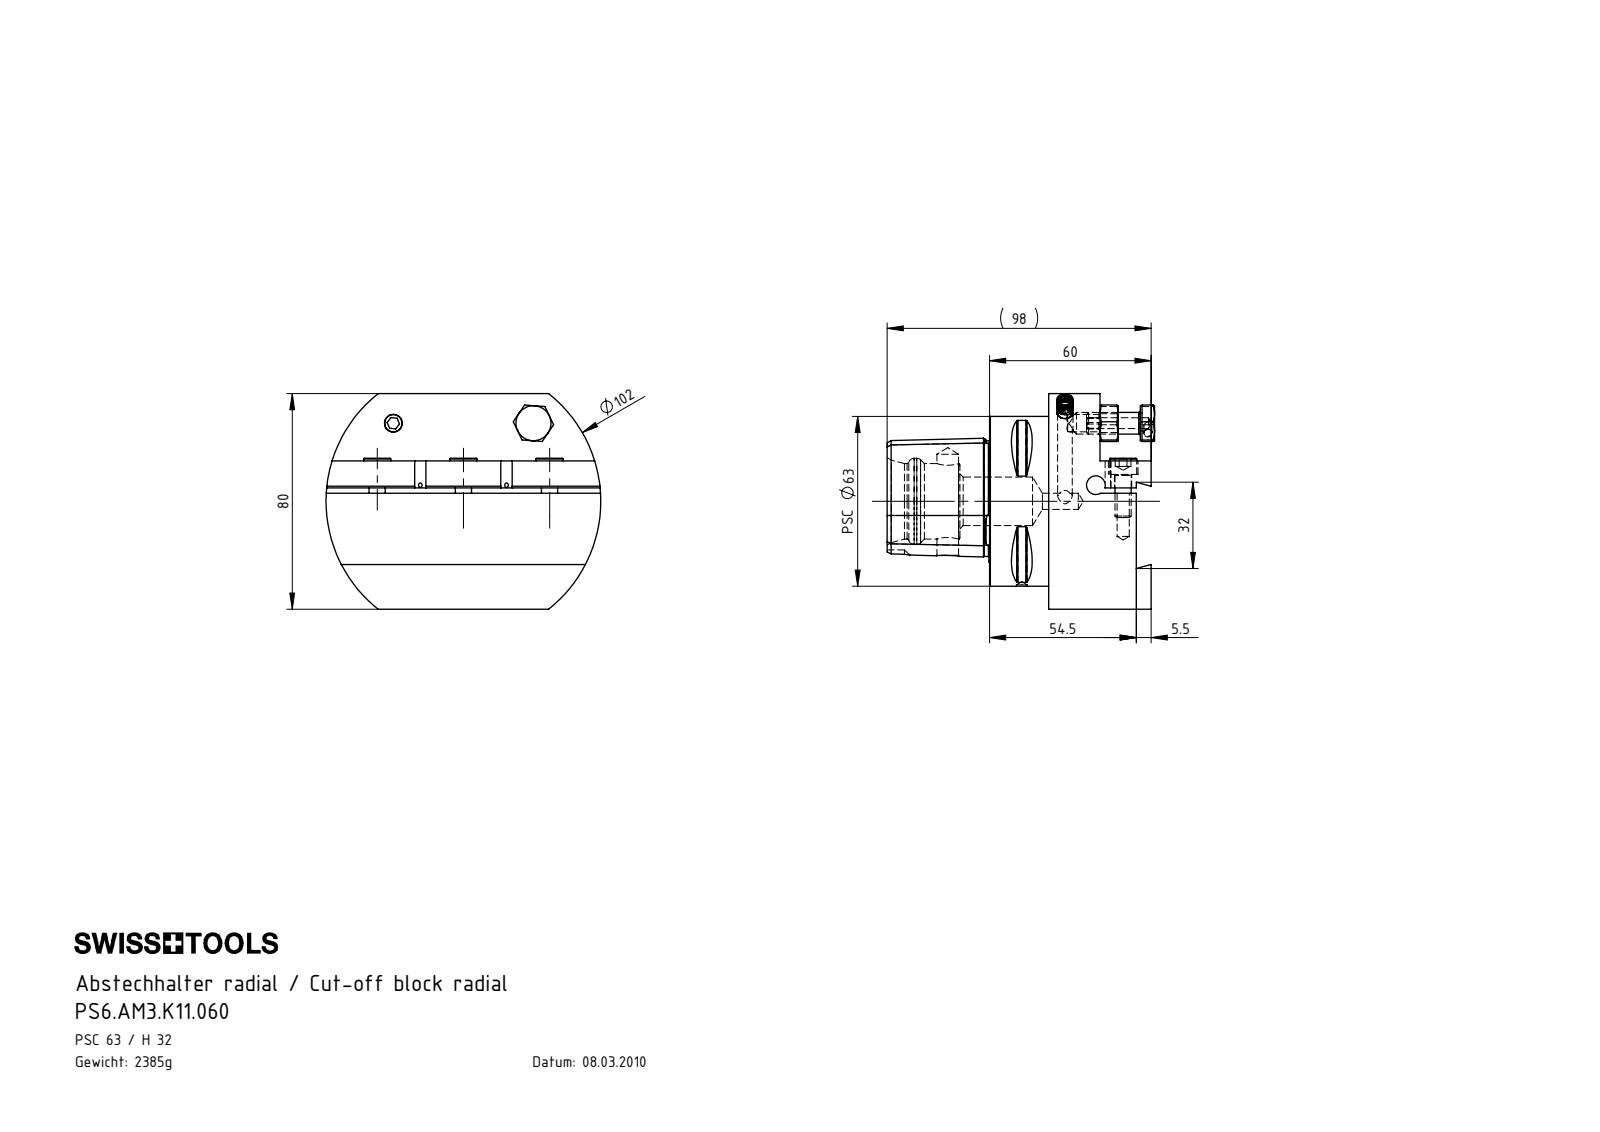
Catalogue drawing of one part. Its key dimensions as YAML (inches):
part_name: "PS6-AM3.K11.060_B; AM3-ER1.001.020_PreviewCfg; KVT_MB_600_060; ISO 4035 - M8_PreviewCfg (+3 more)"
step_written_by: "SolidWorks 2017 (AUTOMOTIVE_DESIGN)"
units: inches
bodies: {solids: 11, faces: 436, planar: 127, cylindrical: 108, other: 201}
overall_size: [4.016, 3.909, 3.15]
volume: 18.57
surface_area: 82.38
round_holes:
  - {diameter: 0.252, count: 5}
  - {diameter: 0.177, count: 3}
  - {diameter: 0.433, count: 3}
  - {diameter: 0.157, count: 2}
  - {diameter: 0.197, count: 2}
  - {diameter: 0.217, count: 2}
  - {diameter: 0.276, count: 2}
  - {diameter: 0.118, count: 1}
  - {diameter: 0.256, count: 1}
  - {diameter: 0.319, count: 1}
  - {diameter: 0.709, count: 1}
  - {diameter: 1.102, count: 1}
round_bosses_or_shafts:
  - {diameter: 0.236, count: 5}
  - {diameter: 0.394, count: 3}
  - {diameter: 0.315, count: 2}
  - {diameter: 2.48, count: 1}
  - {diameter: 0.512, count: 1}
partial_cylinders:
  - {radius: 0.02, count: 8}
  - {radius: 0.083, count: 2}
  - {radius: 0.236, count: 1}
  - {radius: 2.008, count: 1}
face_to_face_distances: [0.748, 1.28, 1.496, 0.217, 0.531, 2.362, 2.165, 1.693, 0.472, 0.866]
hole_center_spacings: [1.26, 1.533, 1.941, 2.852, 1.083, 1.476, 2.047, 2.52]
